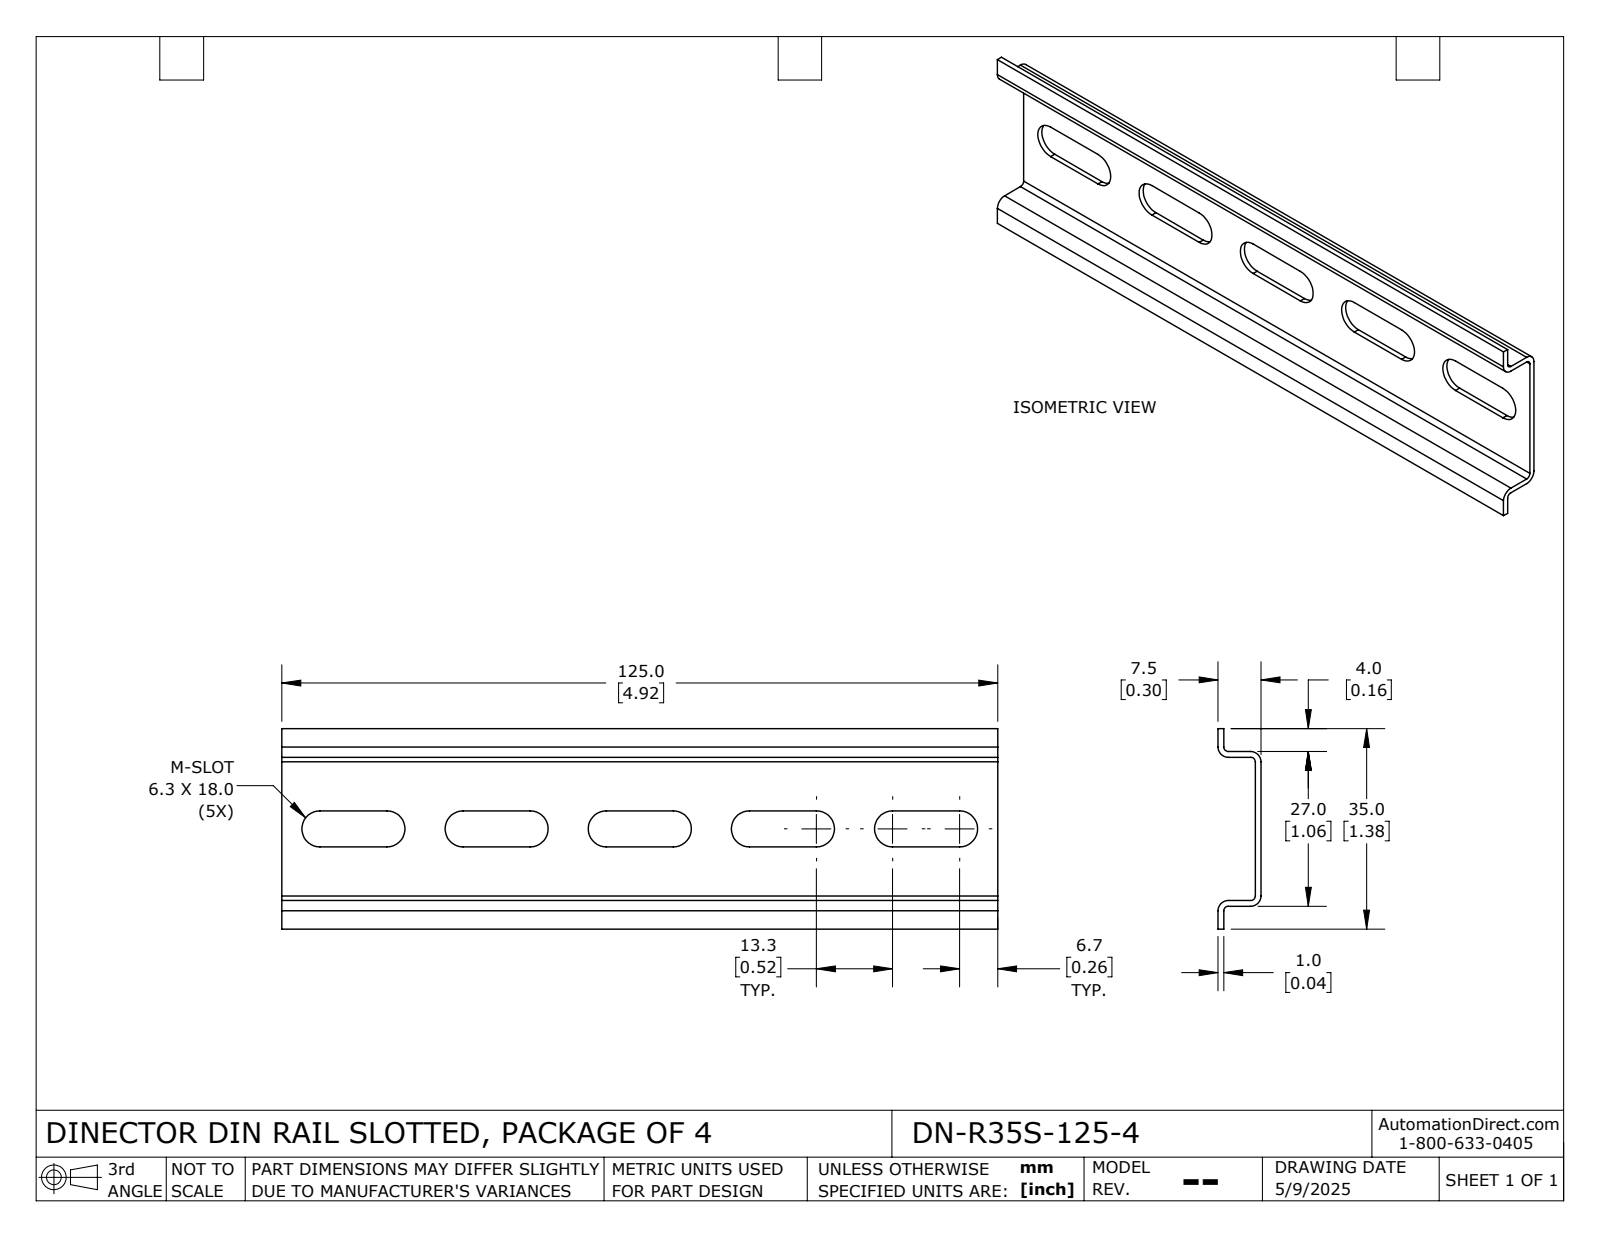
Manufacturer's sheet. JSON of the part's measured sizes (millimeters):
{"part_name": "DN-R35S-125-4_Default", "step_written_by": "SolidWorks 2024 (CONFIG_CONTROL_DESIGN)", "units": "millimeters", "bodies": {"solids": 1, "faces": 42, "planar": 24, "cylindrical": 18, "other": 0}, "overall_size": [125, 35, 7.5], "volume_mm3": 5197, "surface_area_mm2": 10951, "partial_cylinders_radius": [[3.15, 10], [0.8, 4], [1.8, 4]], "face_to_face_distances": [1, 6.5, 26, 7.5, 5.5, 25, 27, 4, 5, 30]}
